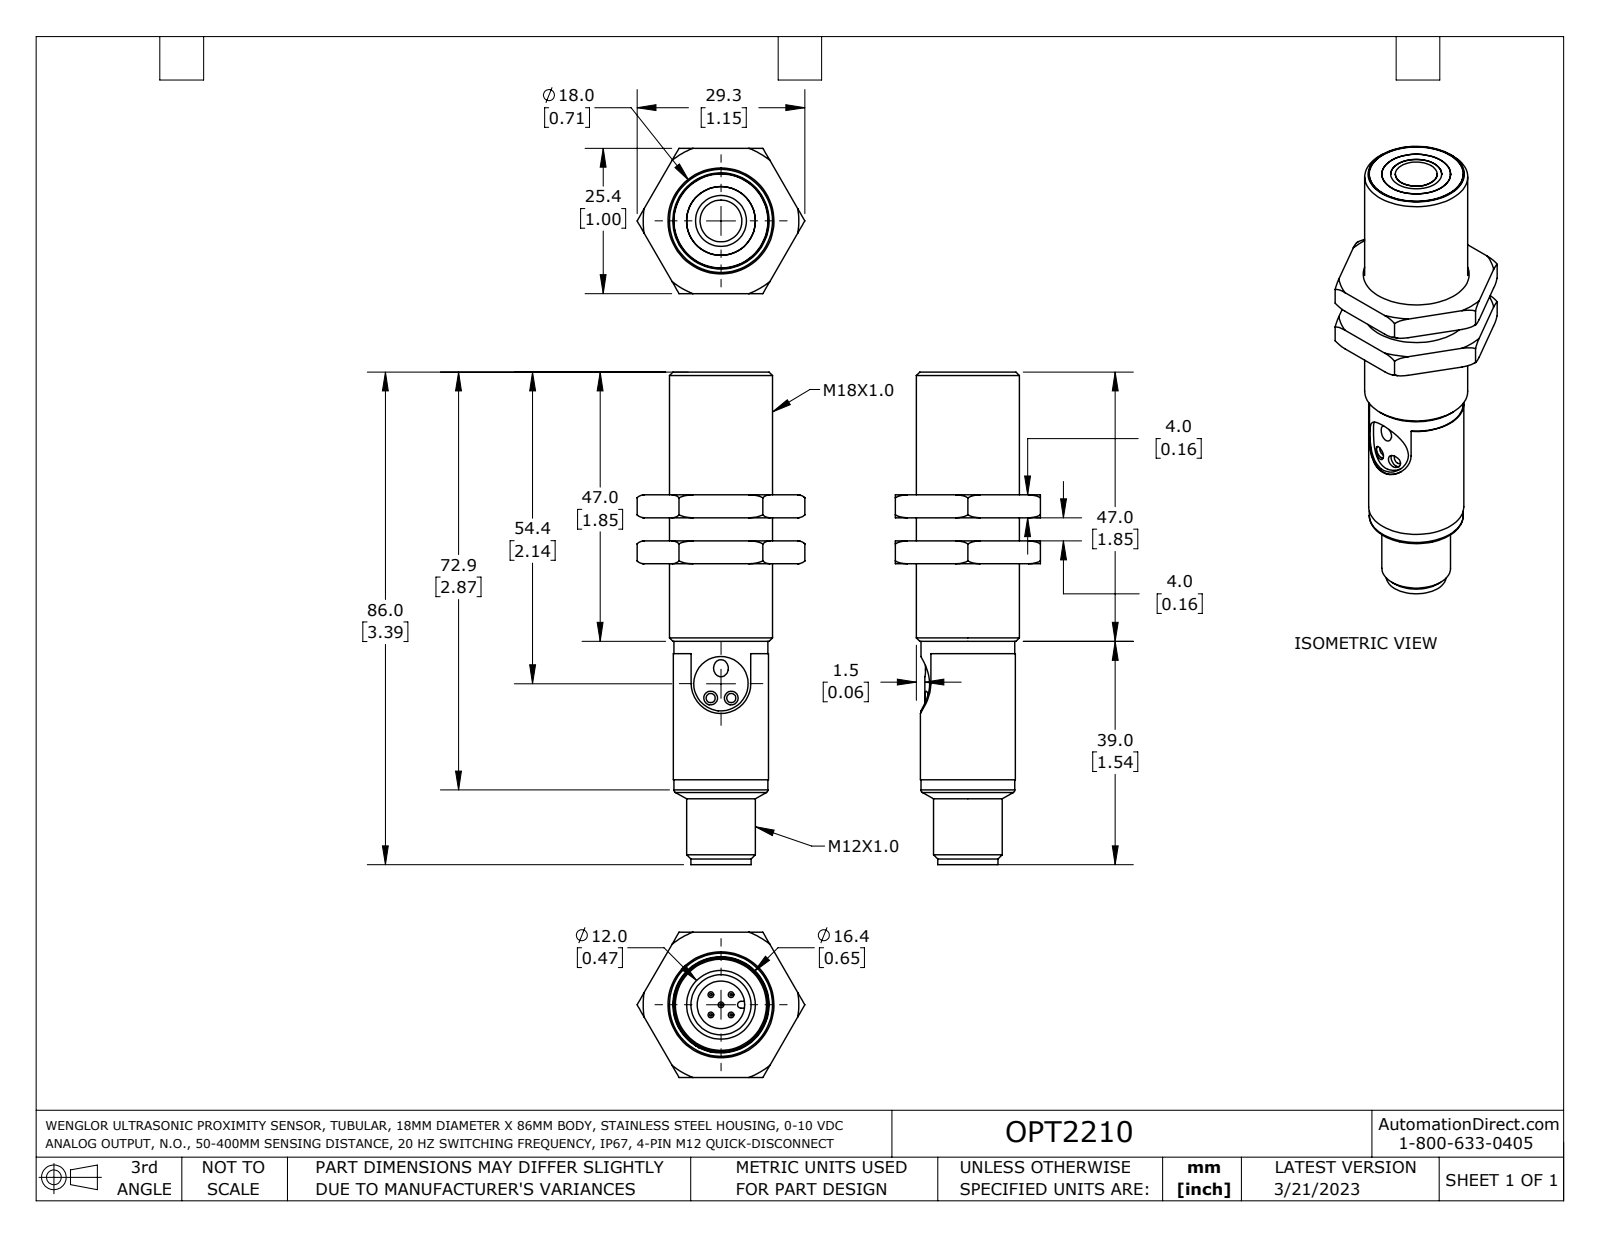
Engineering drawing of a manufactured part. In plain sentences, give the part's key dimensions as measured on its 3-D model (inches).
The part is named "OPT2210". Its 3-D file was written by "SolidWorks 2021 (AUTOMOTIVE_DESIGN)". It is 3 solids with 136 faces: 49 planar, 42 cylindrical and 45 other. Overall it measures 3.386 by 1.153 by 0.998 inches. Its volume is 1.284 cubic inches and its surface area 12.16 square inches. Round holes: 2 of diameter 0.094, 1 of diameter 0.15, 1 of diameter 0.327, 1 of diameter 0.35, 1 of diameter 0.374, 1 of diameter 0.473, 1 of diameter 0.689. Round bosses or shafts: 5 of diameter 0.039, 1 of diameter 0.709, 1 of diameter 0.654, 1 of diameter 0.646, 1 of diameter 0.472, 1 of diameter 0.413, 1 of diameter 0.287. Partial cylindrical surfaces (rounded edges, fillets, slot ends): 4 of radius 0.02, 2 of radius 0.006, 2 of radius 0.051, 1 of radius 0.01, 1 of radius 0.024, 1 of radius 0.067, 1 of radius 0.205, 1 of radius 0.252. The main face-to-face distances are 0.157, 0.317, 0.998, 0.159, 0.474, 1.318, 1.16, 1.001, 0.844, 1.718. The hole center spacings are 0.121, 0.217, 0.106, 0.142.
